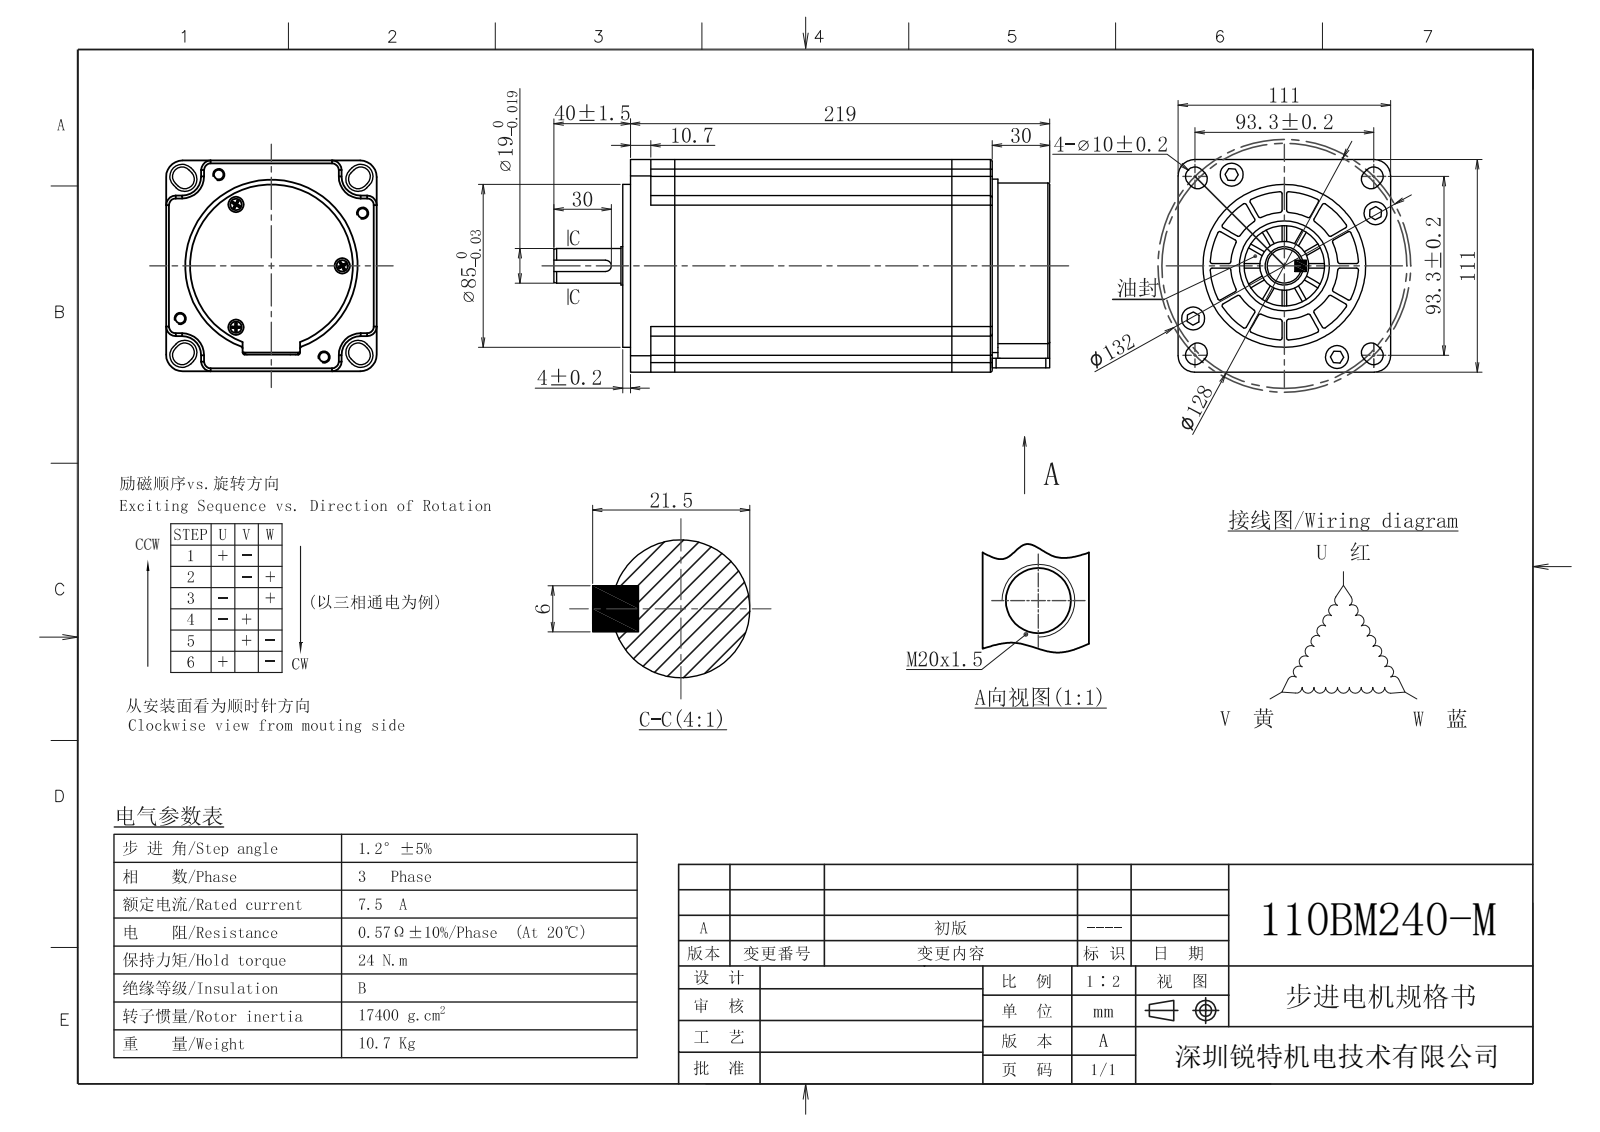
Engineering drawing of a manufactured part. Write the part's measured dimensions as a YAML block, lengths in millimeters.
step_written_by: "SolidWorks 2016 (AUTOMOTIVE_DESIGN)"
units: millimeters
bodies: {solids: 1, faces: 288, planar: 110, cylindrical: 159, other: 19}
overall_size: [259, 111, 111]
volume: 2282000
surface_area: 119152
round_holes:
  - {diameter: 12, count: 4}
  - {diameter: 47, count: 1}
round_bosses_or_shafts:
  - {diameter: 10.5, count: 4}
  - {diameter: 90.5, count: 1}
  - {diameter: 86.5, count: 1}
  - {diameter: 85, count: 1}
  - {diameter: 19.2, count: 1}
  - {diameter: 19, count: 1}
partial_cylinders:
  - {radius: 1, count: 60}
  - {radius: 5, count: 16}
  - {radius: 8.6, count: 4}
  - {radius: 10, count: 4}
  - {radius: 3, count: 2}
  - {radius: 28, count: 1}
  - {radius: 38.75, count: 1}
face_to_face_distances: [111, 219, 18.85, 92.15, 30, 2, 189, 73.3, 4, 223]
hole_center_spacings: [55, 77.78, 110]
